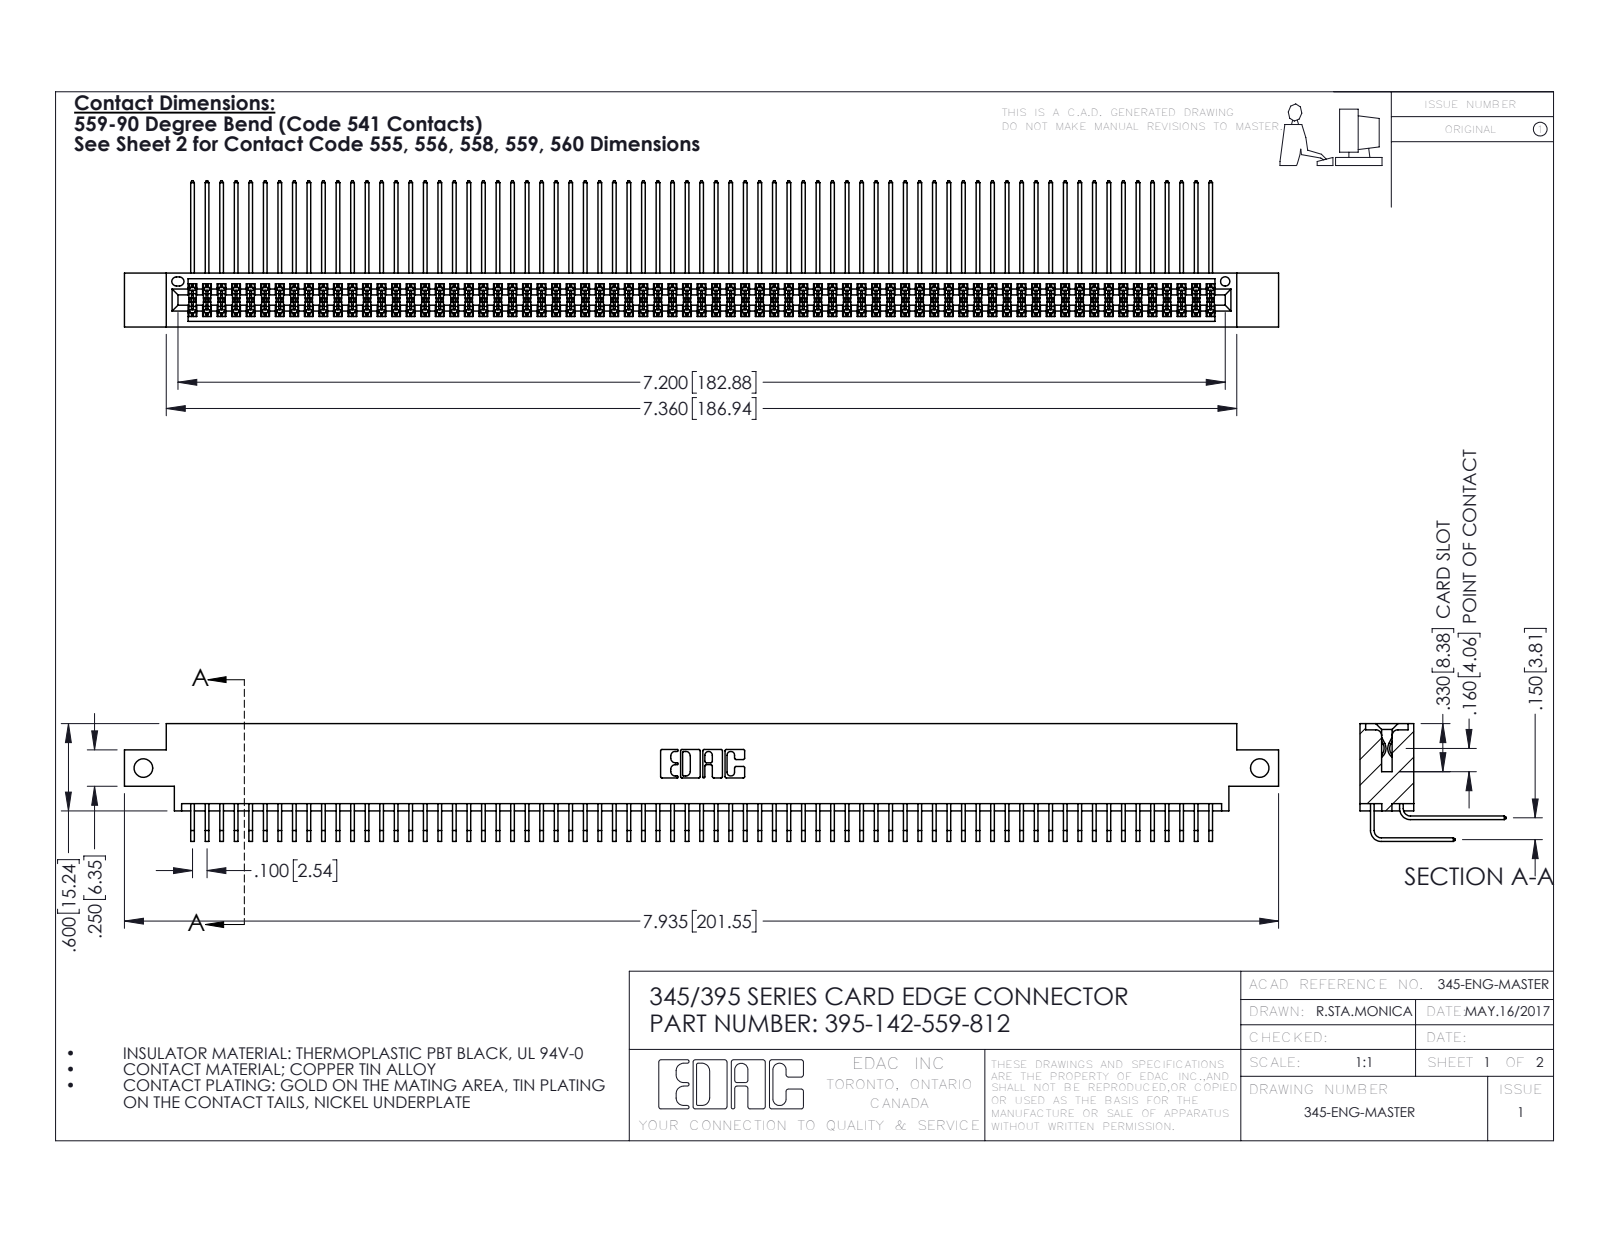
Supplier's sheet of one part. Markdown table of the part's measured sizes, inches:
| quantity | value |
| --- | --- |
| part name | 345-292-001_559 Tail - 2; 345 Part_0.170 Offset - Side Mount; 395-142-559-812; 345-292-001_558 559 Tail - 1 |
| STEP written by | SolidWorks 2016 (CONFIG_CONTROL_DESIGN) |
| units | inches |
| bodies | 143 solids, 7514 faces (5054 planar, 2460 cylindrical, 0 other) |
| overall size | 7.935 × 1.005 × 0.809 |
| volume | 1.249 in³ |
| surface area | 53.75 in² |
| round holes (diameter × count) | 0.128 × 2, 0.064 × 1 |
| partial cylindrical surfaces (radius × count) | 0.006 × 284, 0.01 × 22, 0.007 × 6, 0.031 × 6, 0.026 × 3, 0.014 × 2, 0.019 × 2, 0.022 × 2 |
| main face-to-face distances | 0.072, 0.298, 0.37, 0.2, 0.098, 0.272, 0.025, 0.225, 0.175, 0.15 |
| hole center spacings | 7.675 |
